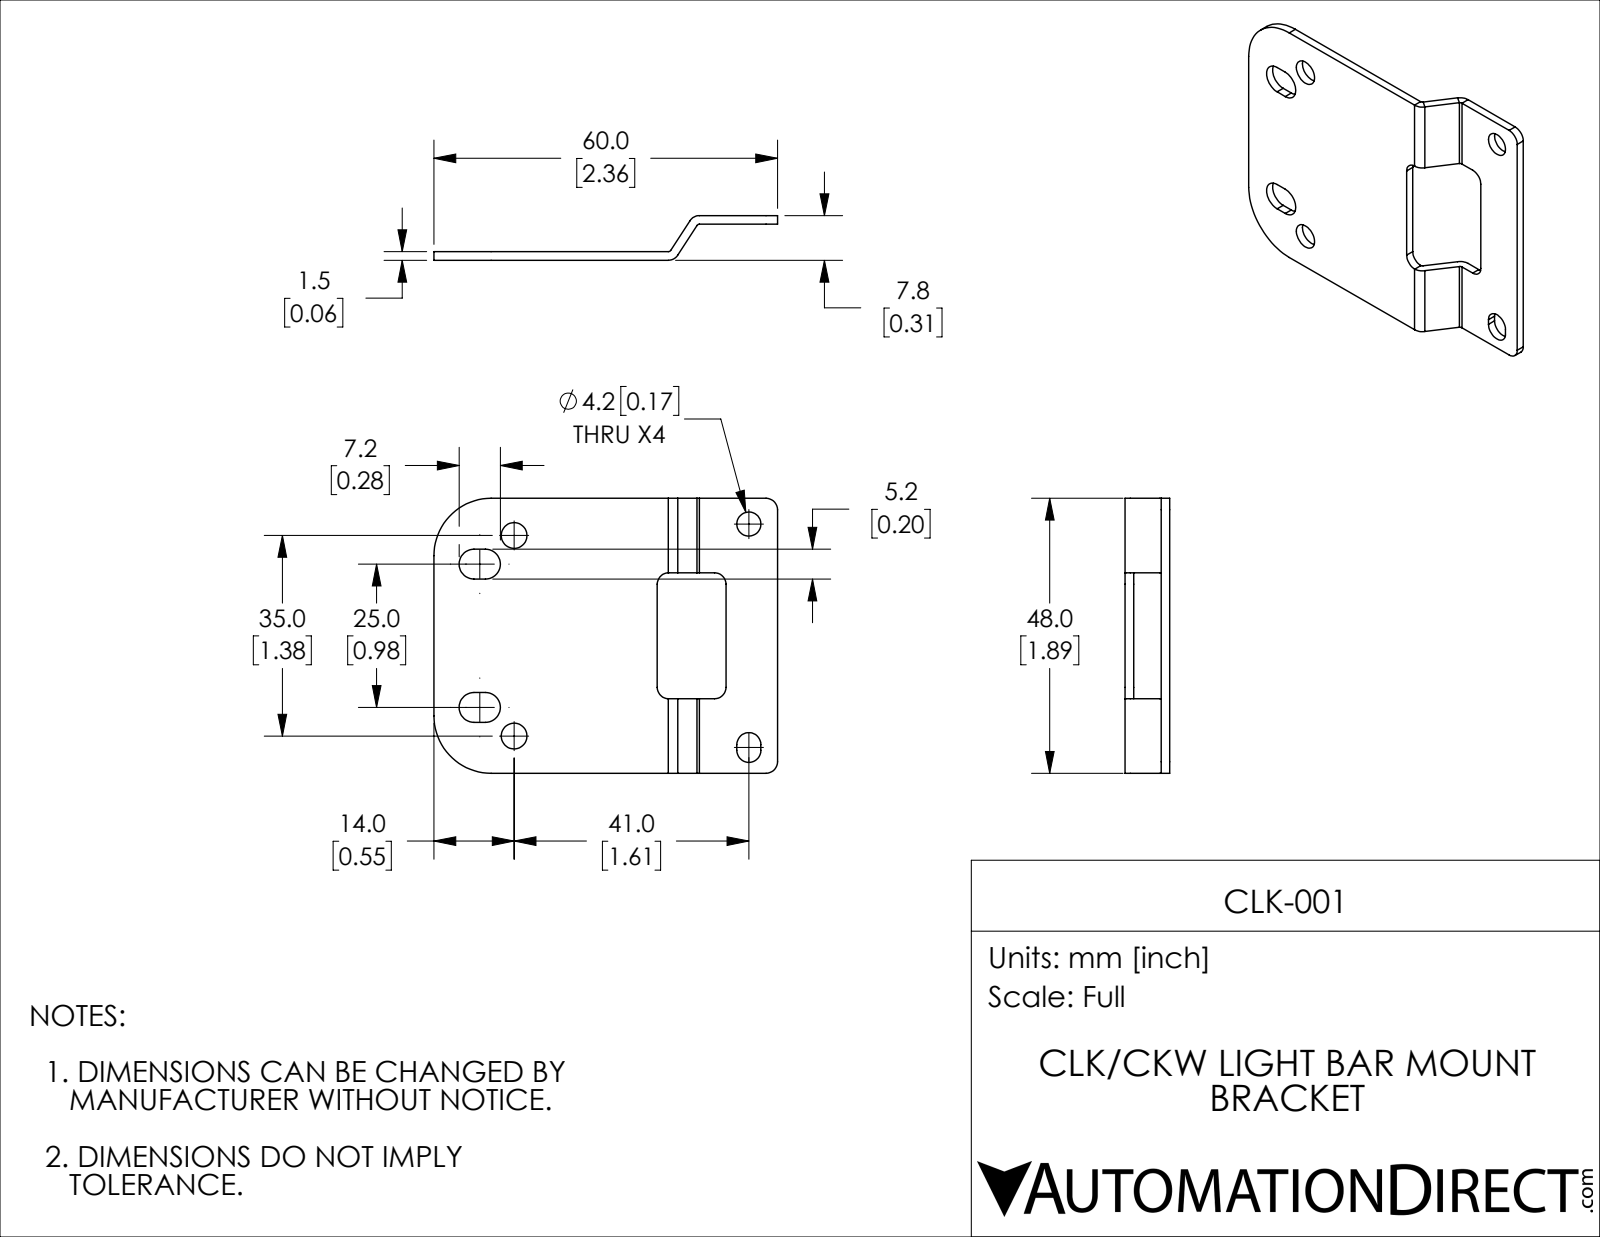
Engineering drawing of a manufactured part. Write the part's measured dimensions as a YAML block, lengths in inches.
part_name: "CLK-001"
step_written_by: "SolidWorks 2018 (AUTOMOTIVE_DESIGN)"
units: inches
bodies: {solids: 1, faces: 60, planar: 30, cylindrical: 30, other: 0}
overall_size: [2.362, 1.89, 0.307]
volume: 0.232
surface_area: 8.73
round_holes:
  - {diameter: 0.177, count: 2}
  - {diameter: 0.165, count: 1}
partial_cylinders:
  - {radius: 0.079, count: 8}
  - {radius: 0.102, count: 4}
  - {radius: 0.02, count: 2}
  - {radius: 0.083, count: 2}
  - {radius: 0.394, count: 2}
face_to_face_distances: [0.059, 0.248, 0.307, 0.189, 1.89, 2.362, 0.512, 1.378, 0.354, 2.008]
hole_center_spacings: [1.378, 1.616, 2.174]
